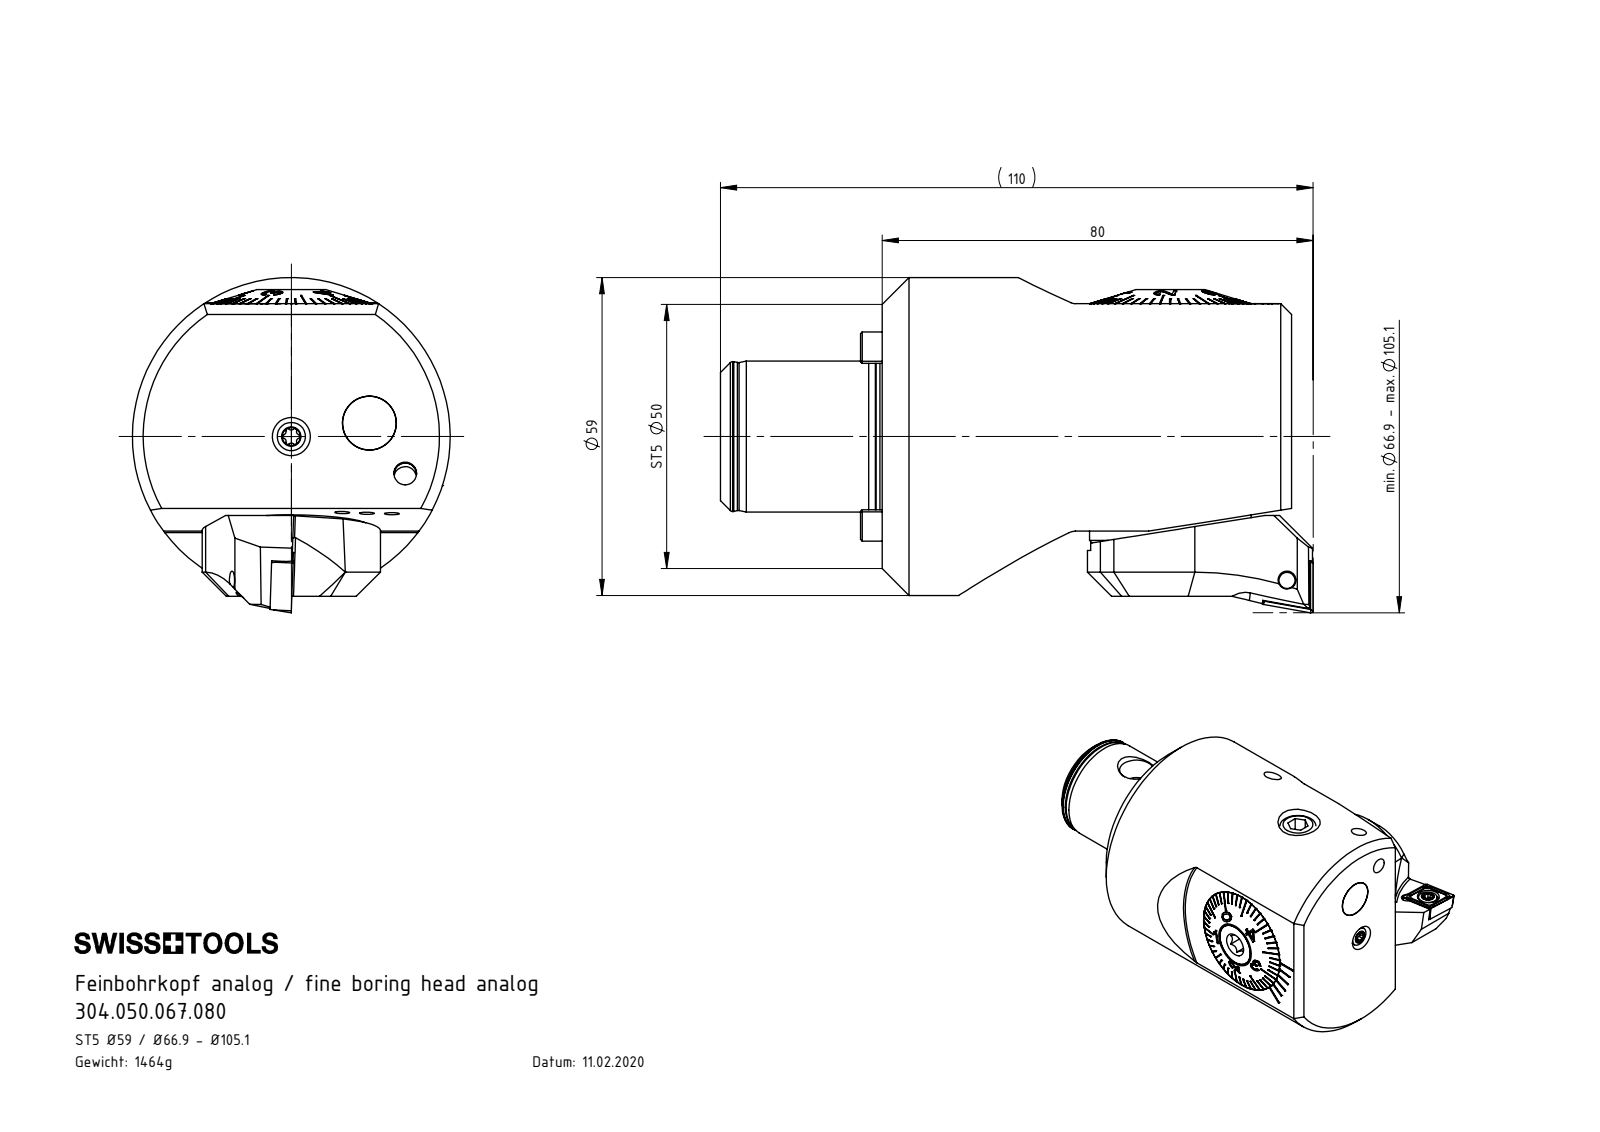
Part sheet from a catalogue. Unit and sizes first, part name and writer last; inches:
Units: inches
Overall size (bounding box): 4.331 × 2.402 × 2.165
Round holes (diameter × count): ⌀0.13 ×7, ⌀0.157 ×2, ⌀0.335 ×2, ⌀0.512 ×2, ⌀0.079 ×1, ⌀0.081 ×1, ⌀0.11 ×1, ⌀0.152 ×1, ⌀0.165 ×1, ⌀0.197 ×1, ⌀0.268 ×1, ⌀0.315 ×1
Round bosses / shafts (diameter × count): ⌀2.165 ×1, ⌀1.18 ×1, ⌀1.177 ×1, ⌀1.102 ×1, ⌀1.094 ×1, ⌀1.075 ×1, ⌀0.984 ×1, ⌀0.709 ×1
Partial cylindrical surfaces — rounded edges, fillets, slot ends (radius × count): R0.008 ×6, R0.013 ×6, R0.02 ×6, R0.023 ×6, R0.014 ×5, R0.039 ×5, R0.126 ×3, R0.176 ×2
Main face-to-face distances: 2.992, 0.28, 1.697, 0.098, 1.417, 1.65, 0.233, 0.046, 0.135, 1.552
Hole centre spacings: 0.665, 0.877, 0.166, 0.17, 0.383, 0.571, 0.824, 0.827
Volume: 11.05 in³ · Surface area: 71.22 in²
Bodies: 17 solids, 884 faces (320 planar, 197 cylindrical, 367 other)
Part name (STEP PRODUCT): WCA-ER2.001.006_A; F55-BG1.012.012_A; F55-BG1.011.036; A55-BG2.012.006_B (+8 more)
STEP written by: SolidWorks 2015 (CONFIG_CONTROL_DESIGN)
